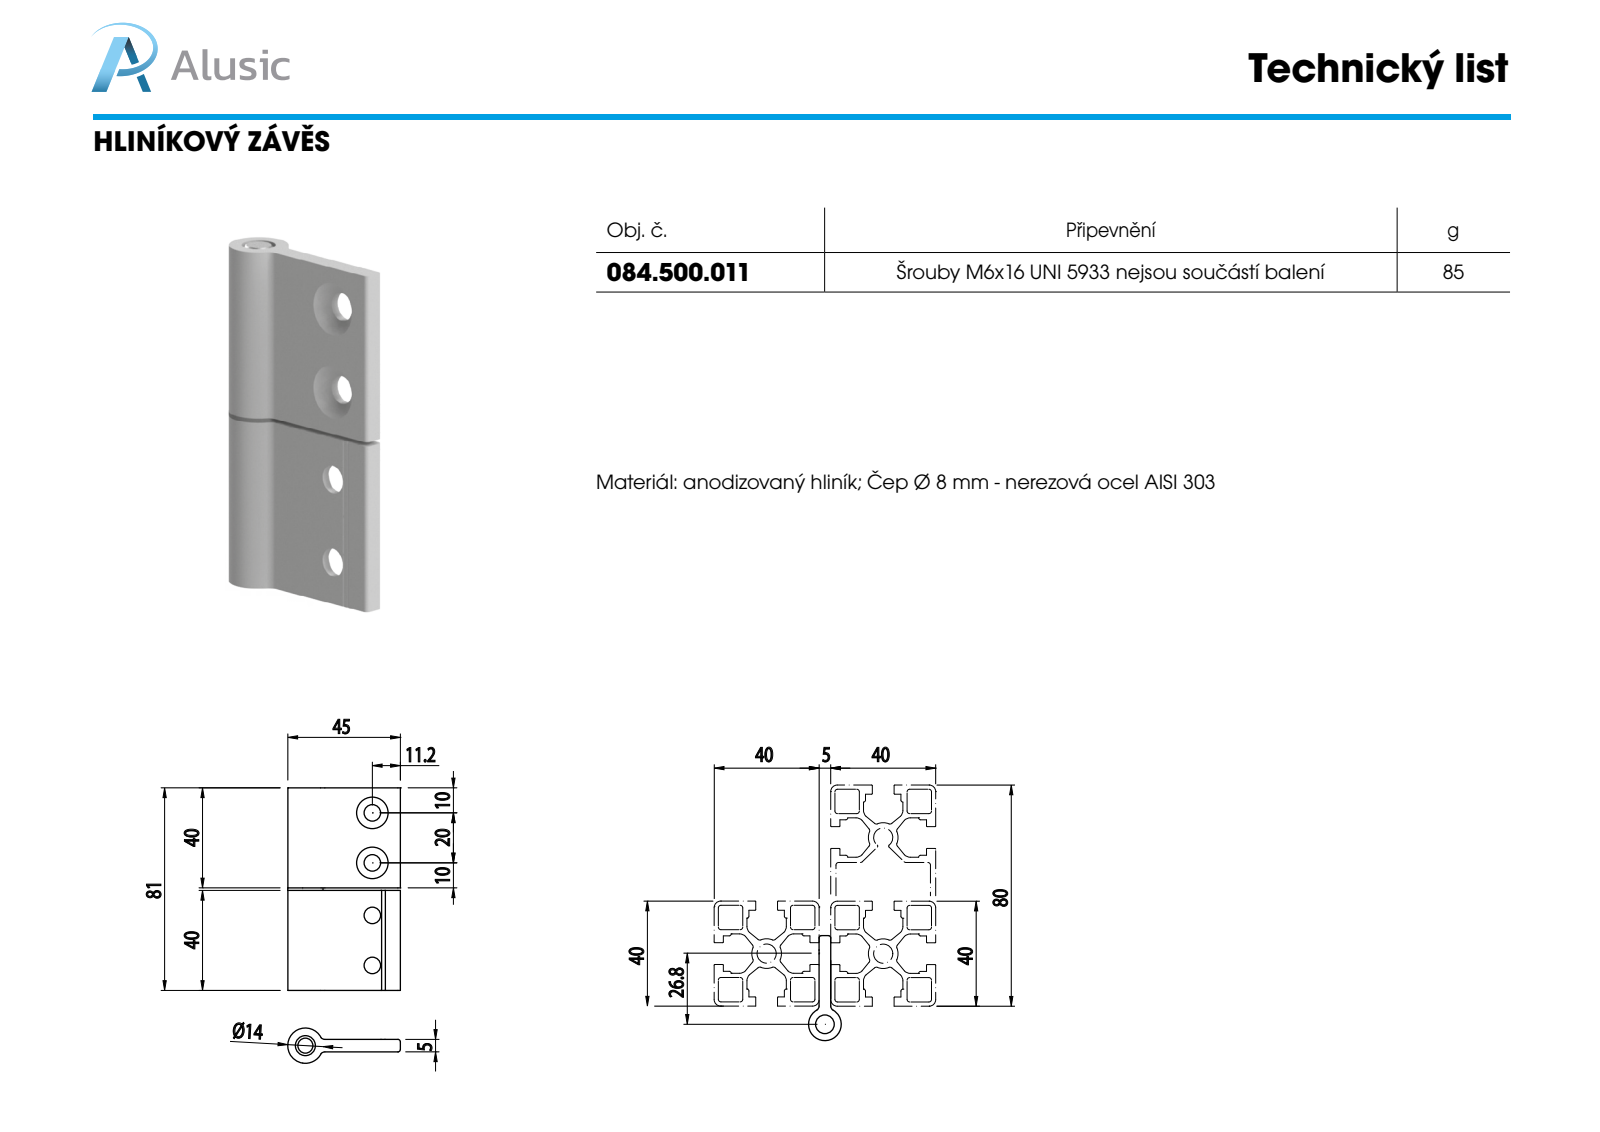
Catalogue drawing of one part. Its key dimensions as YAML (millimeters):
part_name: "084.500.001.C; PERNO CERNIERA_084.500.001.B; 084.500.011L; 084.500.011"
step_written_by: "SolidWorks 2011 (CONFIG_CONTROL_DESIGN)"
units: millimeters
bodies: {solids: 4, faces: 188, planar: 142, cylindrical: 34, other: 12}
overall_size: [81, 45.05, 14.1]
volume: 23726
surface_area: 13977
round_holes:
  - {diameter: 6.6, count: 4}
  - {diameter: 8, count: 1}
  - {diameter: 8.1, count: 1}
round_bosses_or_shafts:
  - {diameter: 14.1, count: 1}
  - {diameter: 14, count: 1}
partial_cylinders:
  - {radius: 0.2, count: 2}
  - {radius: 1, count: 2}
  - {radius: 2, count: 2}
face_to_face_distances: [5, 40, 41, 1, 81, 6.11, 6.12, 3.26, 34.5, 5.5]
hole_center_spacings: [20, 41, 21, 61]
